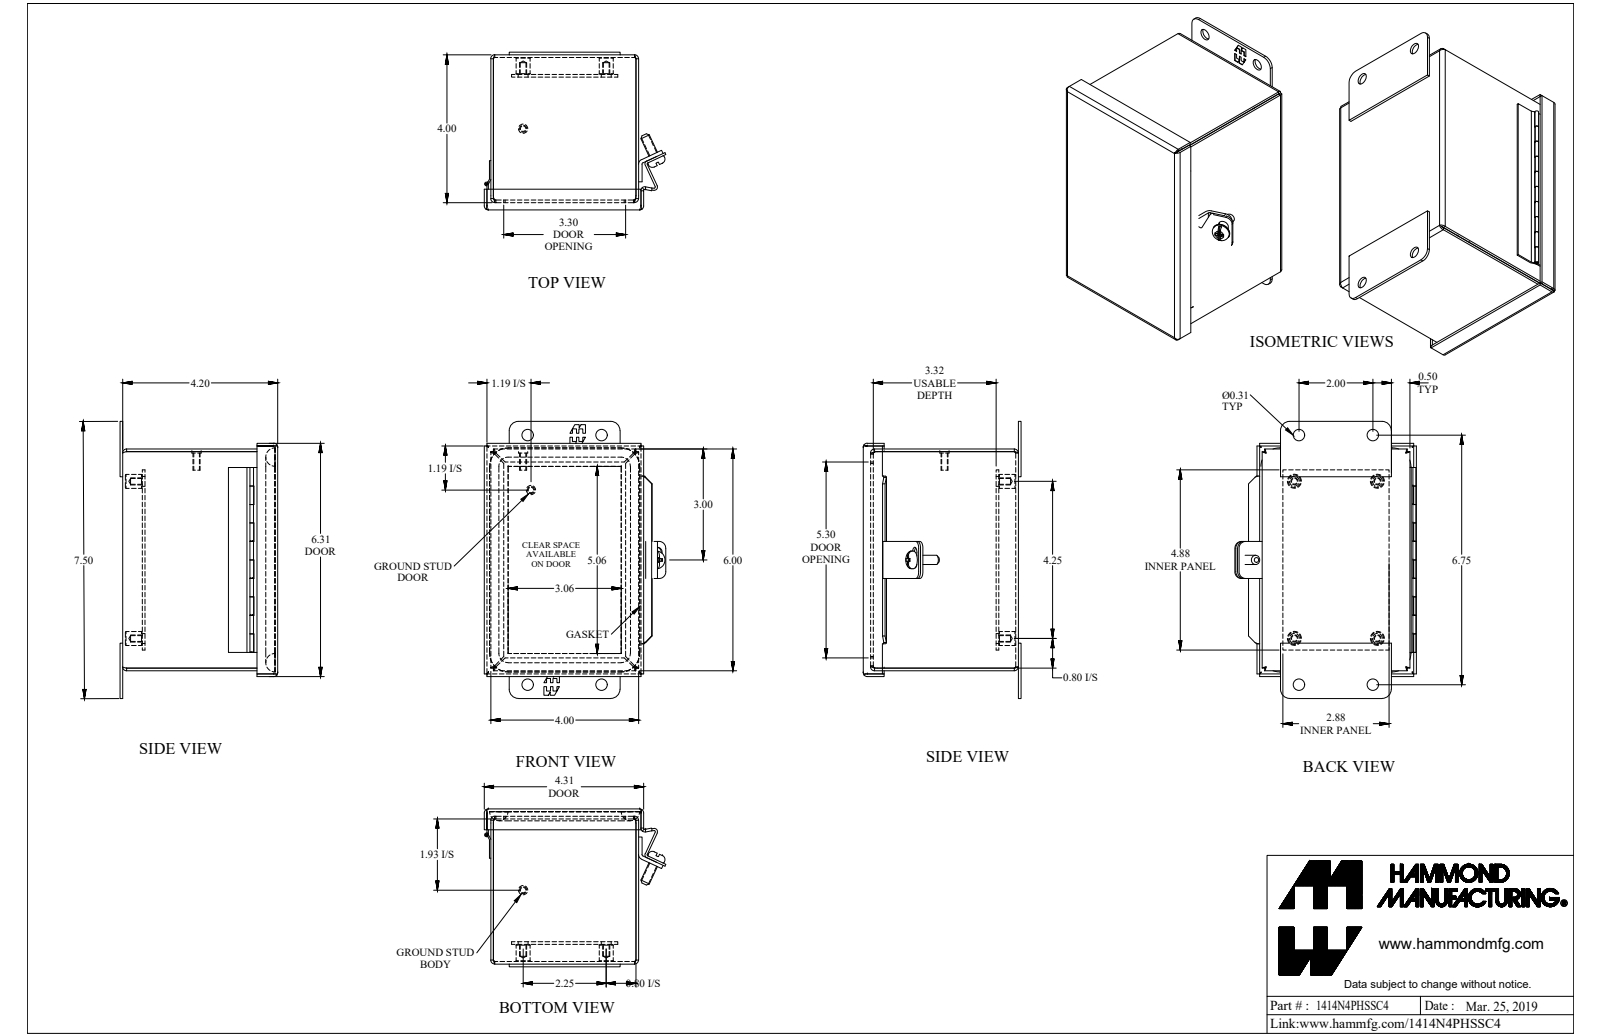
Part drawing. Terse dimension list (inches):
name: 1414N4PHSSC4
written by: SolidWorks 2018 (AUTOMOTIVE_DESIGN)
unit: in
bodies: 17 solids, 458 faces (276 planar, 129 cylindrical, 53 other)
size: 7.5 × 4.903 × 4.269
volume: 26.85 in³; area: 394.8 in²
holes: 4× ⌀0.156, 4× ⌀0.265, 4× ⌀0.313, 1× ⌀0.05, 1× ⌀0.213
bosses: 4× ⌀0.375, 3× ⌀0.25, 2× ⌀0.19, 1× ⌀0.48, 1× ⌀0.1, 1× ⌀0.045
rounds: 20× R0.25, 9× R0.036, 9× R0.108, 4× R0.079, 4× R0.118, 4× R0.188, 4× R0.499, 2× R0.01
face distances: 0.072, 3.928, 4, 5.928, 0.532, 3.856, 3.635, 4.197, 0.562, 4.125
hole spacings: 2.25, 1.257, 4.809, 5.502, 2.465, 2.466, 5.896, 1.256
